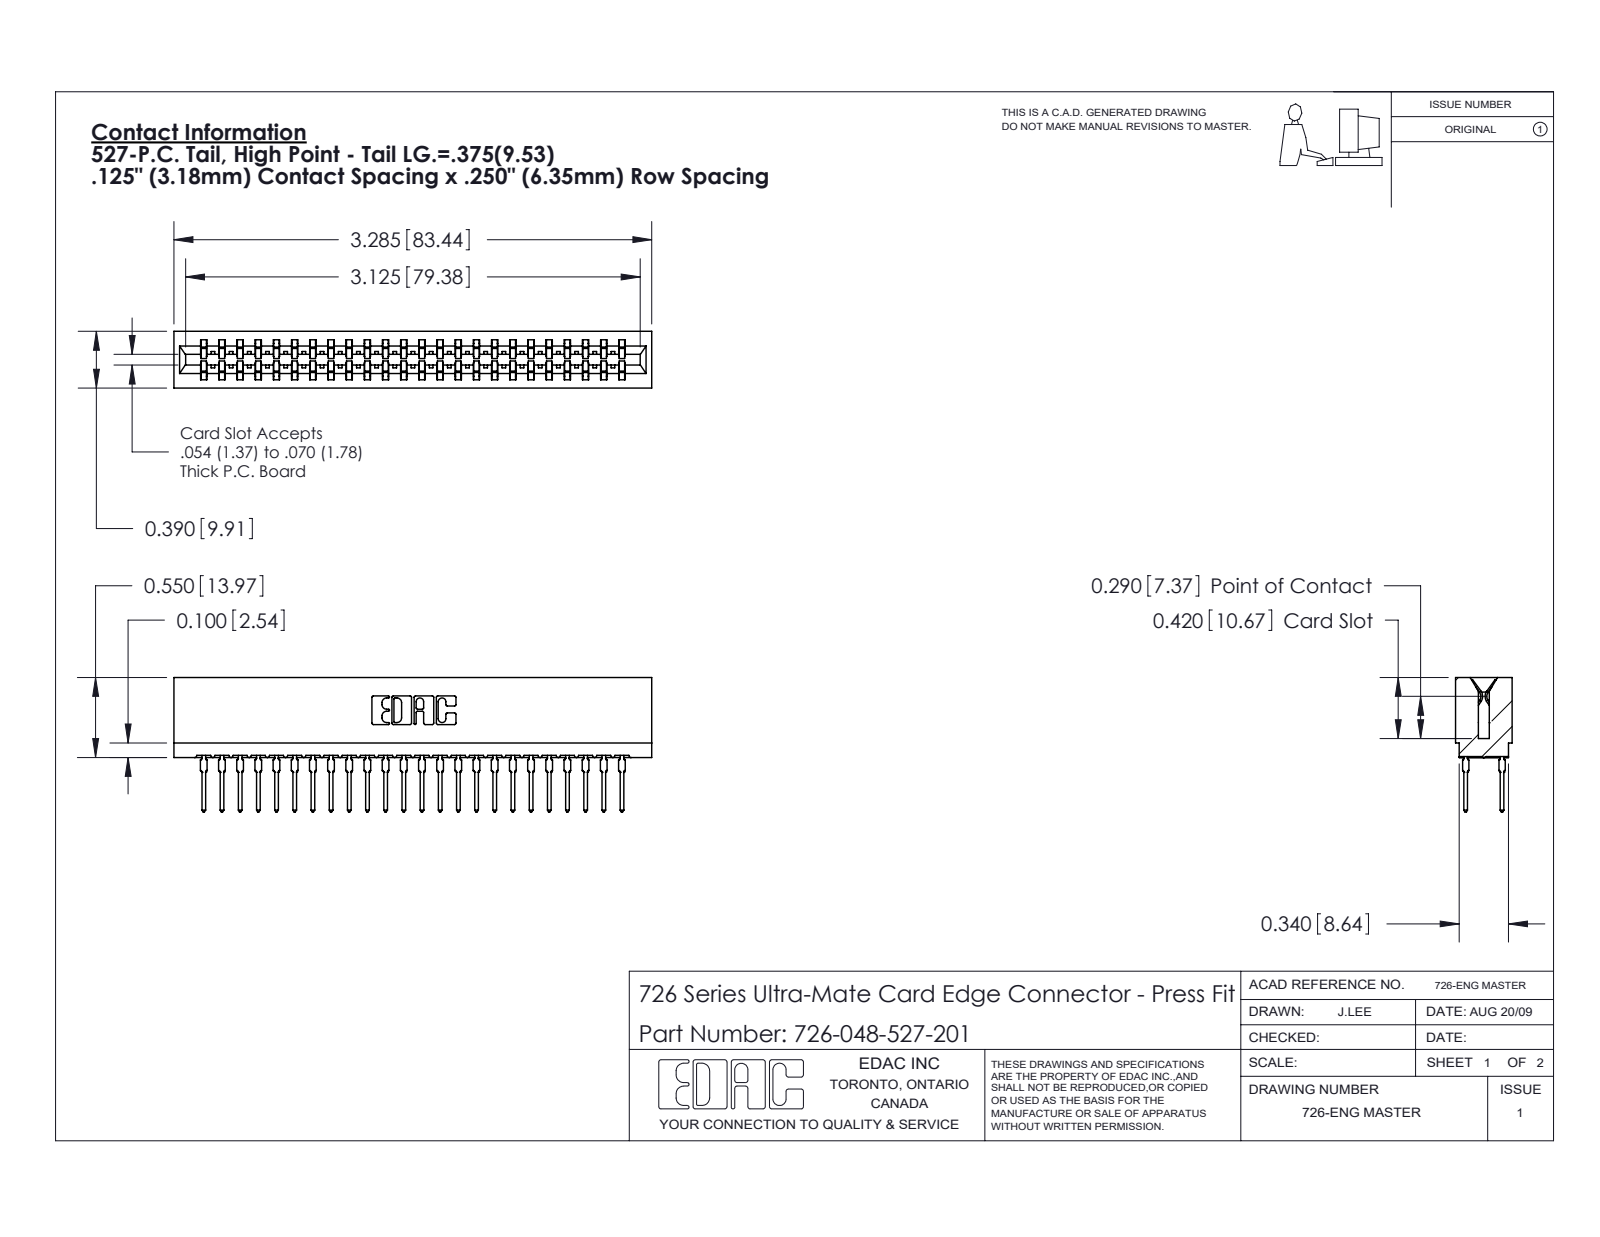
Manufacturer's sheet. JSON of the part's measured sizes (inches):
{"part_name": "726 Part_.515 Slot Depth - 01; 746-292-001_527; 726-048-527-201", "step_written_by": "SolidWorks 2020 (CONFIG_CONTROL_DESIGN)", "units": "inches", "bodies": {"solids": 49, "faces": 4393, "planar": 2263, "cylindrical": 882, "other": 1248}, "overall_size": [3.285, 0.924, 0.39], "volume_in3": 0.479, "surface_area_in2": 20.38, "partial_cylinders_radius": [[0.021, 96], [0.015, 25], [0.01, 22], [0.005, 8], [0.011, 8], [0.007, 6], [0.031, 6], [0.026, 3]], "face_to_face_distances": [0.057, 0.333, 0.025, 0.25, 0.307, 0.39, 0.083, 0.275, 0.042, 0.75]}
